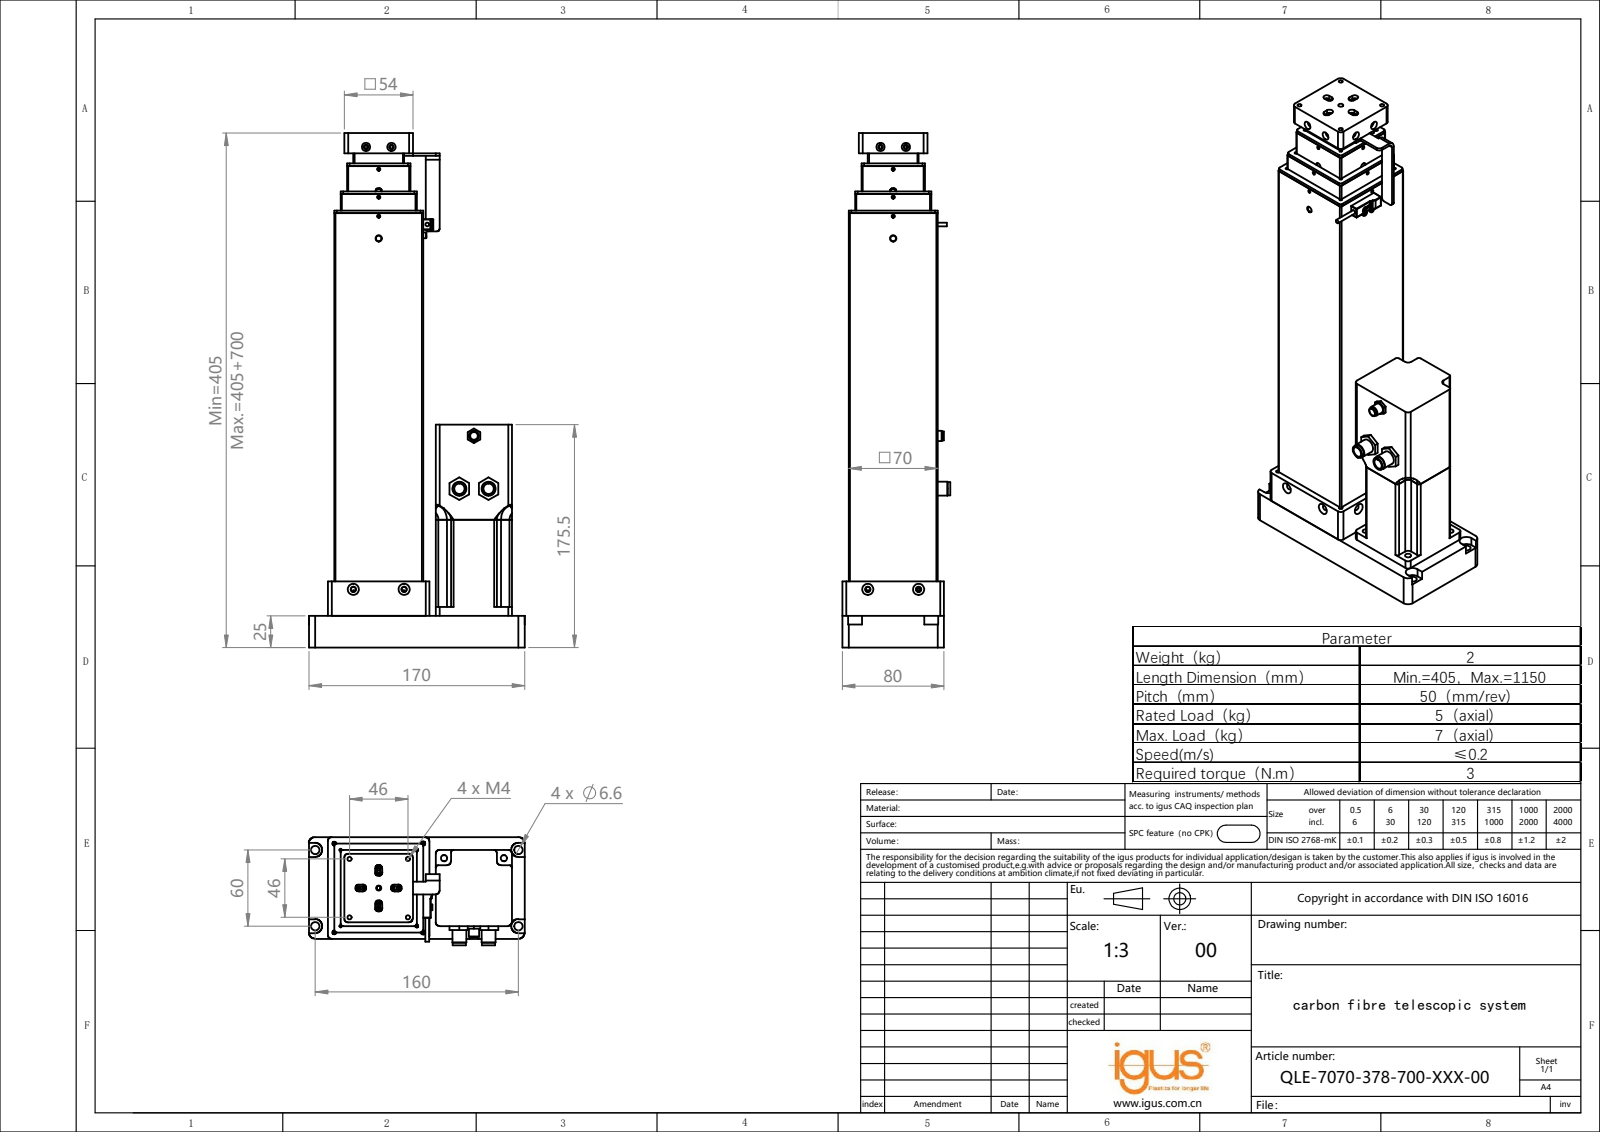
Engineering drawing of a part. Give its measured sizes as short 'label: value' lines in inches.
name: QLE-7070-378-700-XXX-00-2; QLE-7070-378-700-XXX-00; QLE-7070-378-700-XXX-00-1
written by: SolidWorks 2023 (CONFIG_CONTROL_DESIGN)
unit: in
bodies: 159 solids, 5234 faces (1506 planar, 2760 cylindrical, 968 other)
size: 43.504 × 9.15 × 6.693
volume: 205.7 in³; area: 2 714 in²
holes: 59× ⌀0.098, 52× ⌀0.157, 45× ⌀0.118, 36× ⌀0.13, 35× ⌀0.079, 27× ⌀0.197, 25× ⌀0.236, 24× ⌀0.049, 24× ⌀0.063, 24× ⌀0.071, 24× ⌀0.081, 24× ⌀0.134
bosses: 9× ⌀0.276, 8× ⌀0.157, 4× ⌀0.984, 4× ⌀0.433, 4× ⌀0.177, 2× ⌀1.575, 2× ⌀1.5, 2× ⌀1.339
rounds: 98× R0.118, 88× R0.03, 88× R0.039, 84× R0.079, 32× R0.012, 26× R0.197, 16× R0.057, 16× R0.059
face distances: 0.098, 0.197, 0.295, 2.362, 2.264, 2.461, 2.165, 0.394, 2.067, 2.559
hole spacings: 0.787, 0.531, 0.689, 0.794, 0.335, 0.581, 1.245, 1.328
